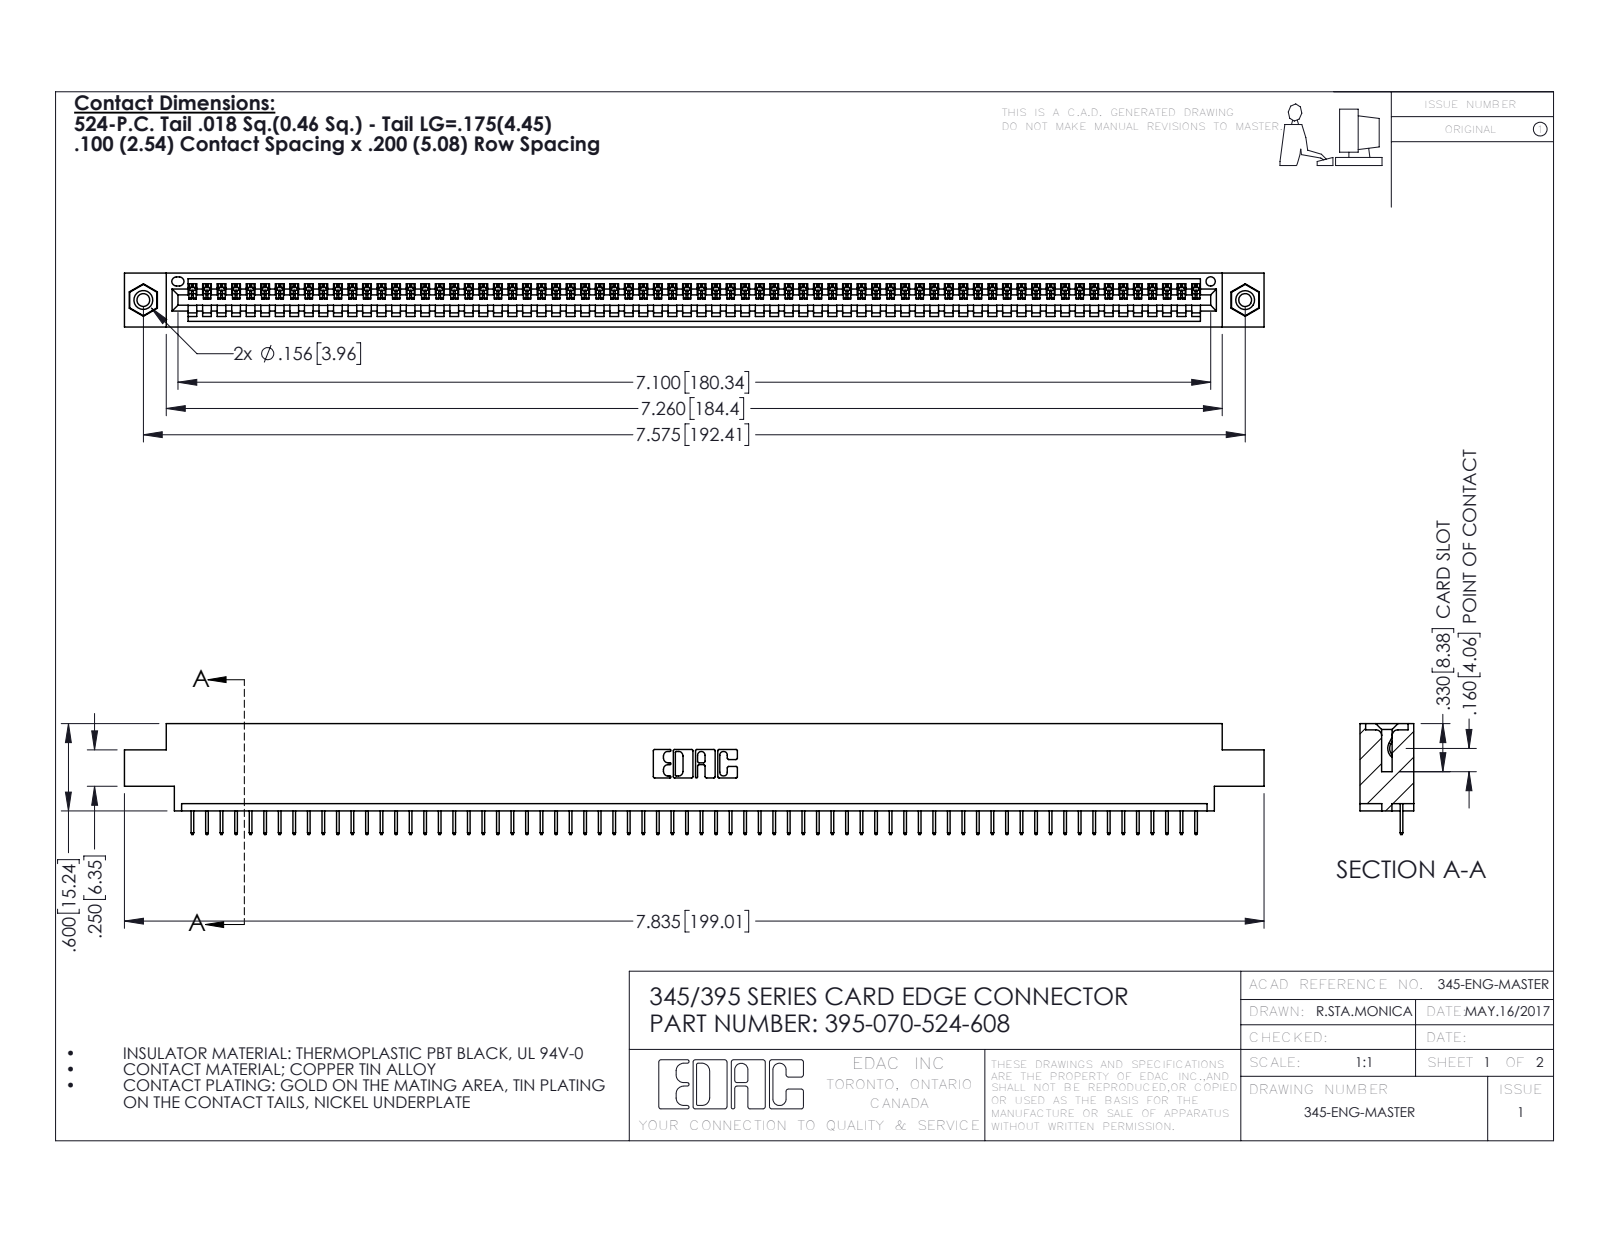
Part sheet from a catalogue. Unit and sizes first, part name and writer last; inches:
Units: inches
Overall size (bounding box): 7.835 × 0.762 × 0.37
Round holes (diameter × count): ⌀0.089 ×2, ⌀0.125 ×2, ⌀0.156 ×2, ⌀0.064 ×1
Round bosses / shafts (diameter × count): ⌀0.155 ×2
Partial cylindrical surfaces — rounded edges, fillets, slot ends (radius × count): R0.006 ×140, R0.01 ×22, R0.007 ×6, R0.031 ×6, R0.026 ×3, R0.031 ×2, R0.04 ×2, R0.014 ×1
Main face-to-face distances: 0.072, 0.298, 0.37, 0.2, 0.098, 0.272, 0.025, 0.225, 0.072, 0.175
Hole centre spacings: 0.27, 7.339, 7.575
Volume: 1.143 in³ · Surface area: 38.04 in²
Bodies: 73 solids, 4530 faces (3336 planar, 1178 cylindrical, 16 other)
Part name (STEP PRODUCT): 395-070-524-608; 345-250-001_345-250-003-102; 345-292-001_345-293-124; 345 Part_0.170 Offset - 0.156 Dia-TI
STEP written by: SolidWorks 2016 (CONFIG_CONTROL_DESIGN)
